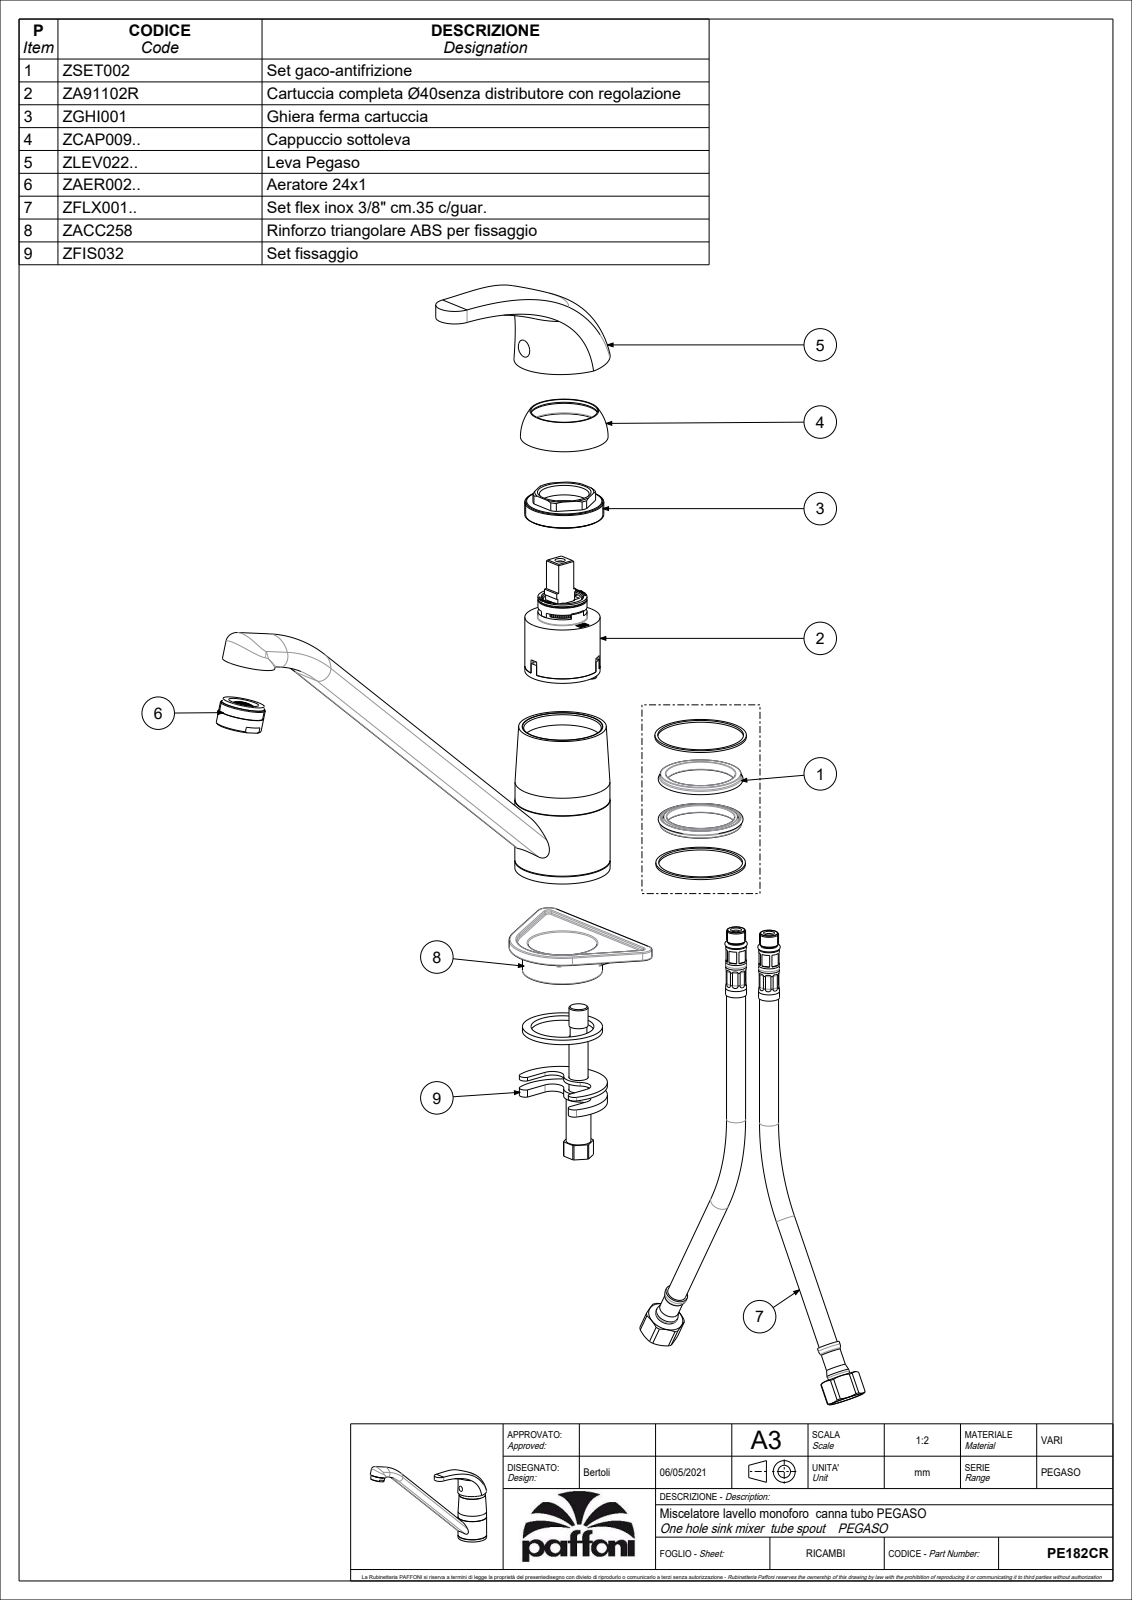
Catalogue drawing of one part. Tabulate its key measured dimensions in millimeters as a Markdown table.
| quantity | value |
| --- | --- |
| part name | PE182CR_SW0001 |
| STEP written by | CREO PARAMETRIC BY PTC INC, 2022124 (CONFIG_CONTROL_DESIGN) |
| units | millimeters |
| bodies | 1 solid, 187 faces (54 planar, 85 cylindrical, 48 other) |
| overall size | 253.52 × 182.37 × 51.37 |
| volume | 276 941 mm³ |
| surface area | 65 799 mm² |
| round holes (diameter × count) | 9 × 3, 6 × 1, 11 × 1, 11.6 × 1, 44 × 1, 45 × 1, 47.5 × 1, 48.2 × 1 |
| round bosses / shafts (diameter × count) | 50 × 1, 49.8 × 1, 48 × 1, 46.5 × 1, 44.8 × 1, 43.7 × 1, 40.5 × 1, 37 × 1 |
| partial cylindrical surfaces (radius × count) | 1 × 8, 5.5 × 4, 16.5 × 2, 3.9 × 1, 24.93 × 1, 110.52 × 1 |
| main face-to-face distances | 7.5, 17, 93.4, 19.5, 2.5, 115.92, 22.52, 18.4, 27.9, 9.5 |
| hole center spacings | 0.4, 0.5, 1, 1.5, 6, 6.5, 7.5, 72.8 |
